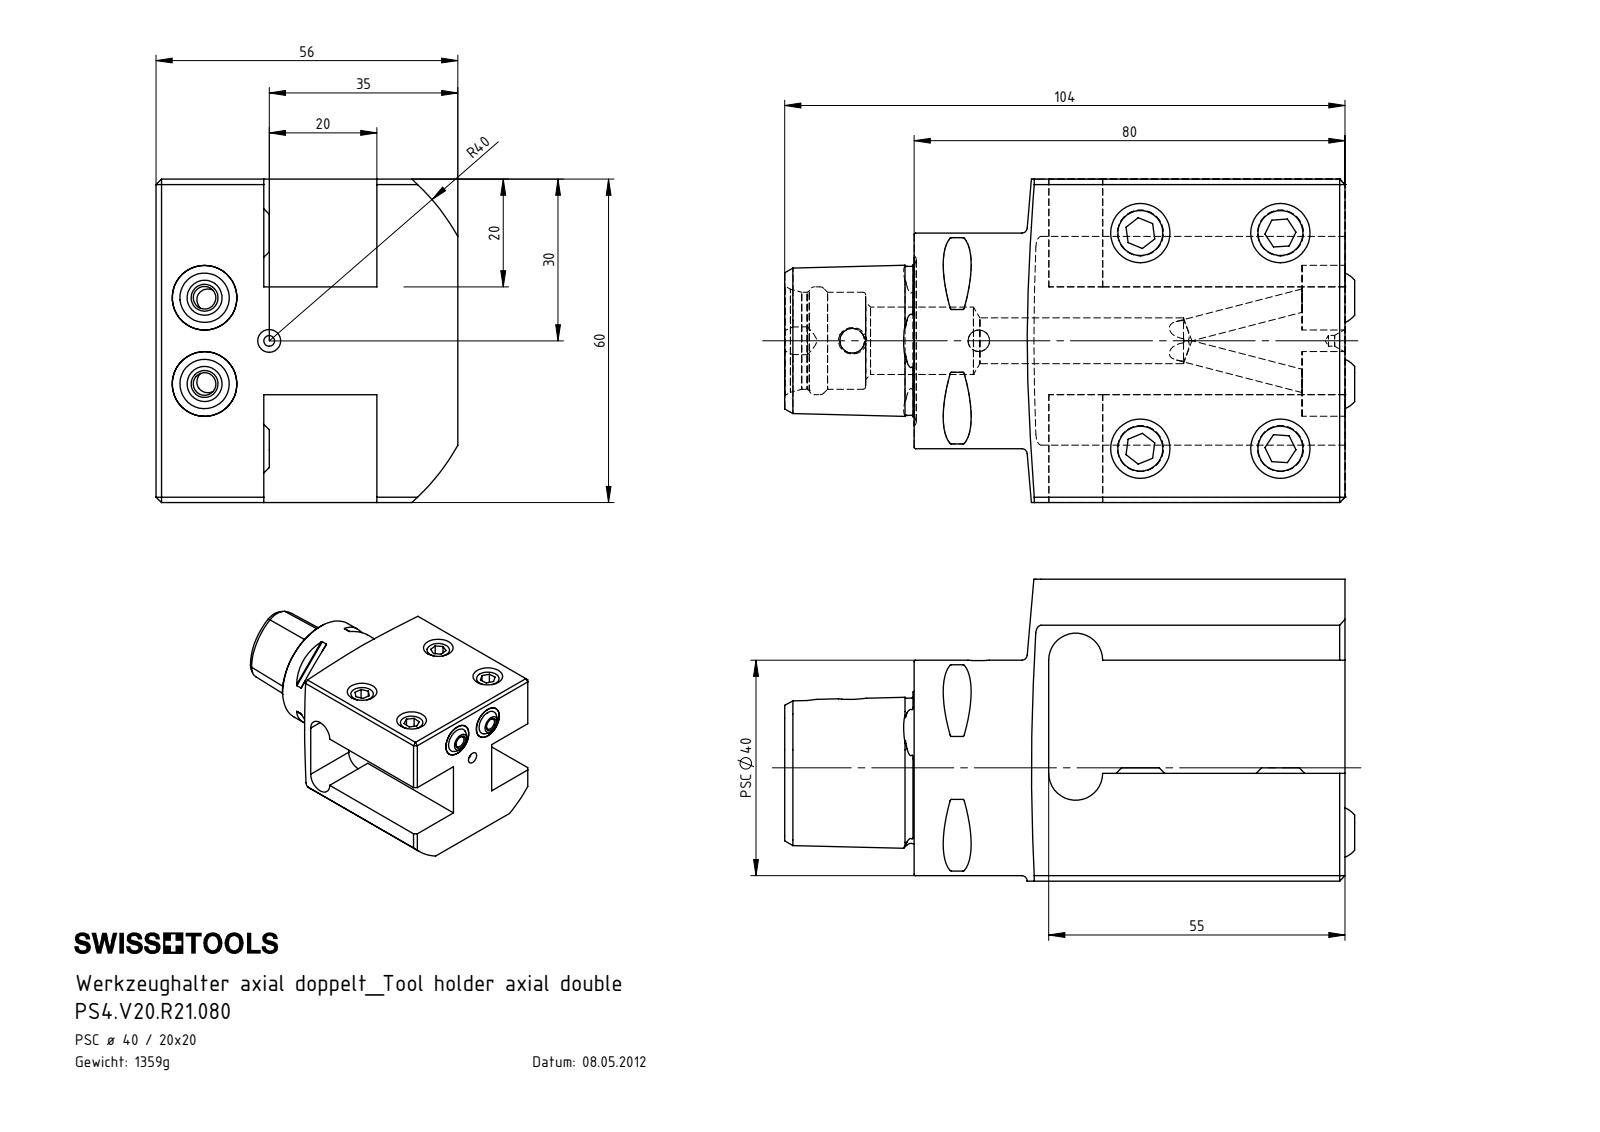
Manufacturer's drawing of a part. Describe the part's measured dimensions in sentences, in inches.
The part is named "PS4.V20.R21.080; KU1-U12.001.010; KU1-U12.001.010_2; PS4-V20.R21.080_A (+2 more)". Its 3-D file was written by "SolidWorks 2017 (AUTOMOTIVE_DESIGN)". It is 9 solids with 290 faces: 84 planar, 73 cylindrical and 133 other. Overall it measures 4.165 by 2.362 by 2.205 inches. Its volume is 10.6 cubic inches and its surface area 61.6 square inches. Round holes: 5 of diameter 0.335, 4 of diameter 0.165, 2 of diameter 0.276, 2 of diameter 0.472, 1 of diameter 0.079, 1 of diameter 0.157, 1 of diameter 0.181, 1 of diameter 0.492, 1 of diameter 0.709, 1 of diameter 0.787. Round bosses or shafts: 4 of diameter 0.394, 1 of diameter 1.575. Partial cylindrical surfaces (rounded edges, fillets, slot ends): 8 of radius 0.012, 2 of radius 0.197, 1 of radius 0.118, 1 of radius 1.575. The main face-to-face distances are 0.787, 1.575, 2.205, 0.591, 1.614, 0.827, 1.417, 2.362, 2.165, 0.984. The hole center spacings are 0.568, 1.024, 1.42, 1.575, 1.878, 2.249, 2.341, 3.228.
